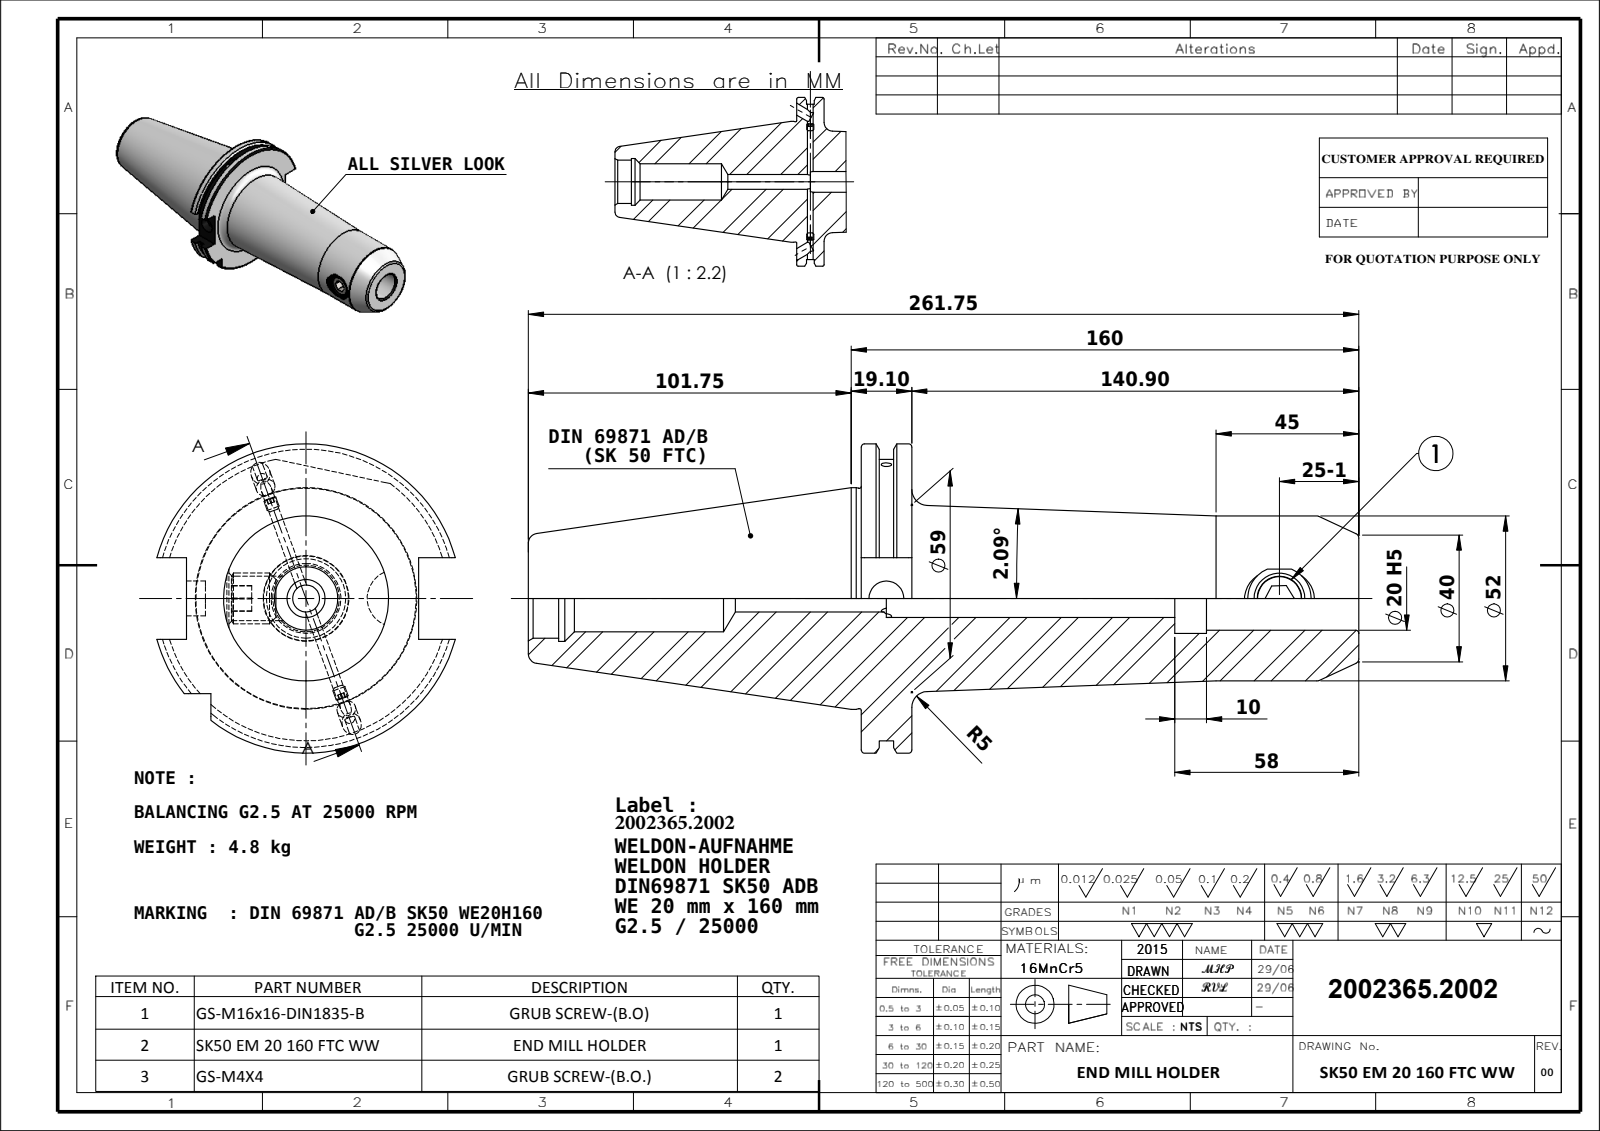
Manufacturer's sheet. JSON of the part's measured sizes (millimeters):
{"part_name": "M16X16_ISO 4026 - M16 x 10-N; 91506-WE720160; SK50 EM 20 160 FTC WW; M4X4_DIN 913 - M4 x 4-N", "step_written_by": "SolidWorks 2009 (CONFIG_CONTROL_DESIGN)", "units": "millimeters", "bodies": {"solids": 4, "faces": 174, "planar": 55, "cylindrical": 57, "other": 62}, "overall_size": [261.75, 97.5, 94.05], "volume_mm3": 627439, "surface_area_mm2": 74156, "round_holes": [[6, 2], [3.3, 1], [8.5, 1], [11, 1], [12, 1], [14, 1], [20, 1], [21, 1], [22, 1], [25, 1], [27, 1]], "round_bosses_or_shafts": [[4, 2], [69.85, 1], [69.45, 1], [52, 1], [16, 1]], "partial_cylinders_radius": [[10, 1], [44.9, 1], [48.75, 1]], "face_to_face_distances": [15.9, 156.8, 140.9, 5.66, 10.24, 151.14, 10.15, 4.49, 5.75, 146.65], "hole_center_spacings": [123.9]}
